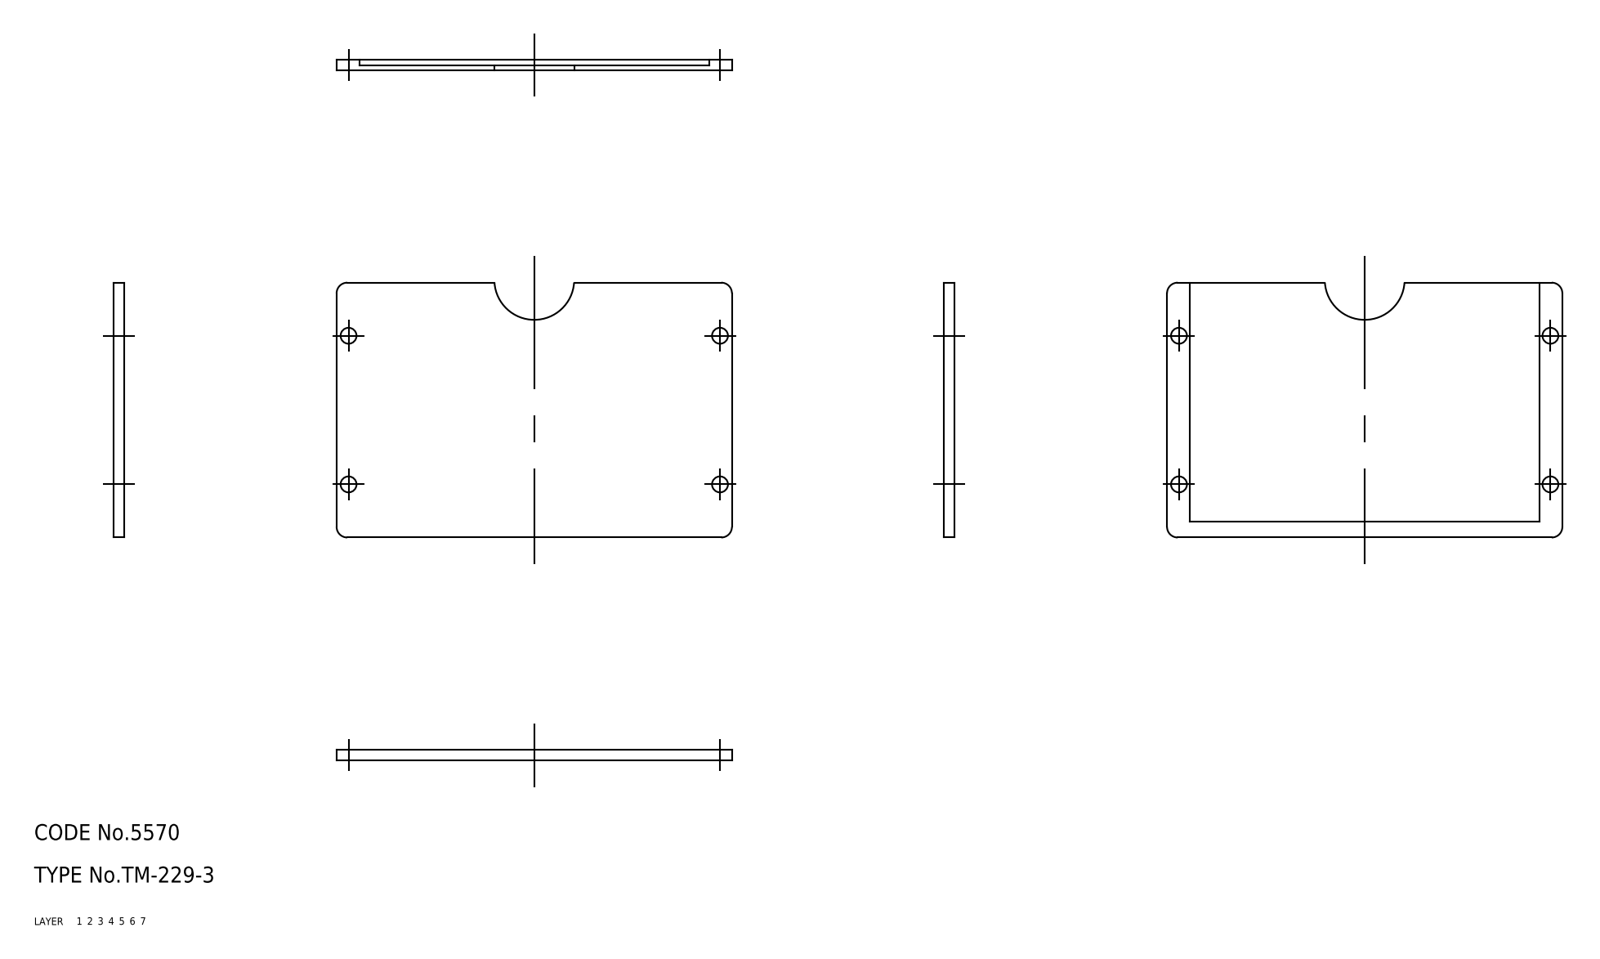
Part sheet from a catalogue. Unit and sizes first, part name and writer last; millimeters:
Units: millimetres
Overall size (bounding box): 74.5 × 48 × 2
Volume: 4 037 mm³ · Surface area: 7 583 mm²
Bodies: 1 solid, 24 faces (0 planar, 0 cylindrical, 24 other)
Part name (STEP PRODUCT): holder
STEP written by: CADfix (AUTOMOTIVE_DESIGN)
